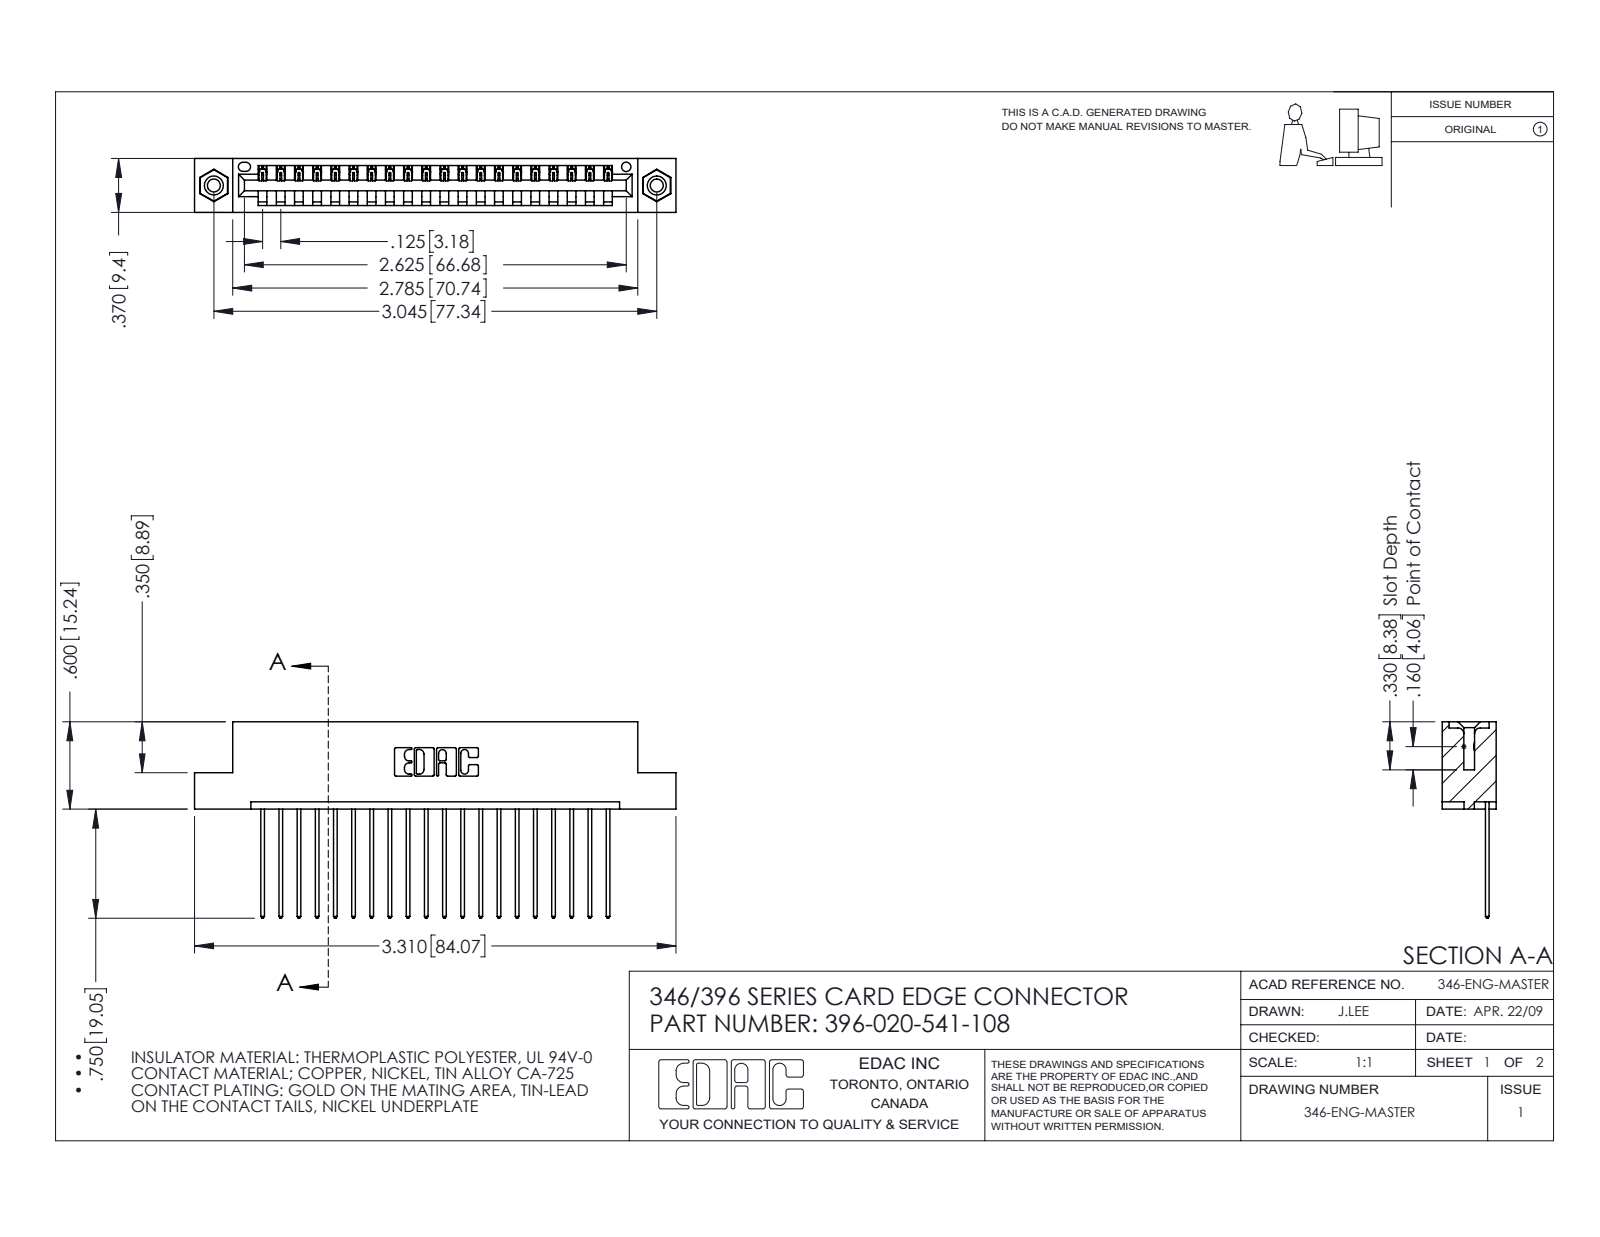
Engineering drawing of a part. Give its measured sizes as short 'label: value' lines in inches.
name: 345-292-001_345-293-141; 345-250-001_345-250-003-102; 396-020-541-108; 346 Part_Flush Mounting Lugs - 0.156 Dia-TI
written by: SolidWorks 2016 (CONFIG_CONTROL_DESIGN)
unit: in
bodies: 23 solids, 1342 faces (908 planar, 418 cylindrical, 16 other)
size: 3.31 × 1.35 × 0.37
volume: 0.485 in³; area: 15.69 in²
holes: 2× ⌀0.089, 2× ⌀0.125, 2× ⌀0.156, 1× ⌀0.064
bosses: 2× ⌀0.155
rounds: 40× R0.006, 40× R0.01, 22× R0.01, 6× R0.007, 6× R0.031, 3× R0.026, 2× R0.031, 2× R0.04
face distances: 0.048, 0.322, 0.25, 0.37, 0.072, 0.298, 0.025, 0.148, 0.222, 0.1
hole spacings: 0.246, 2.837, 3.045
